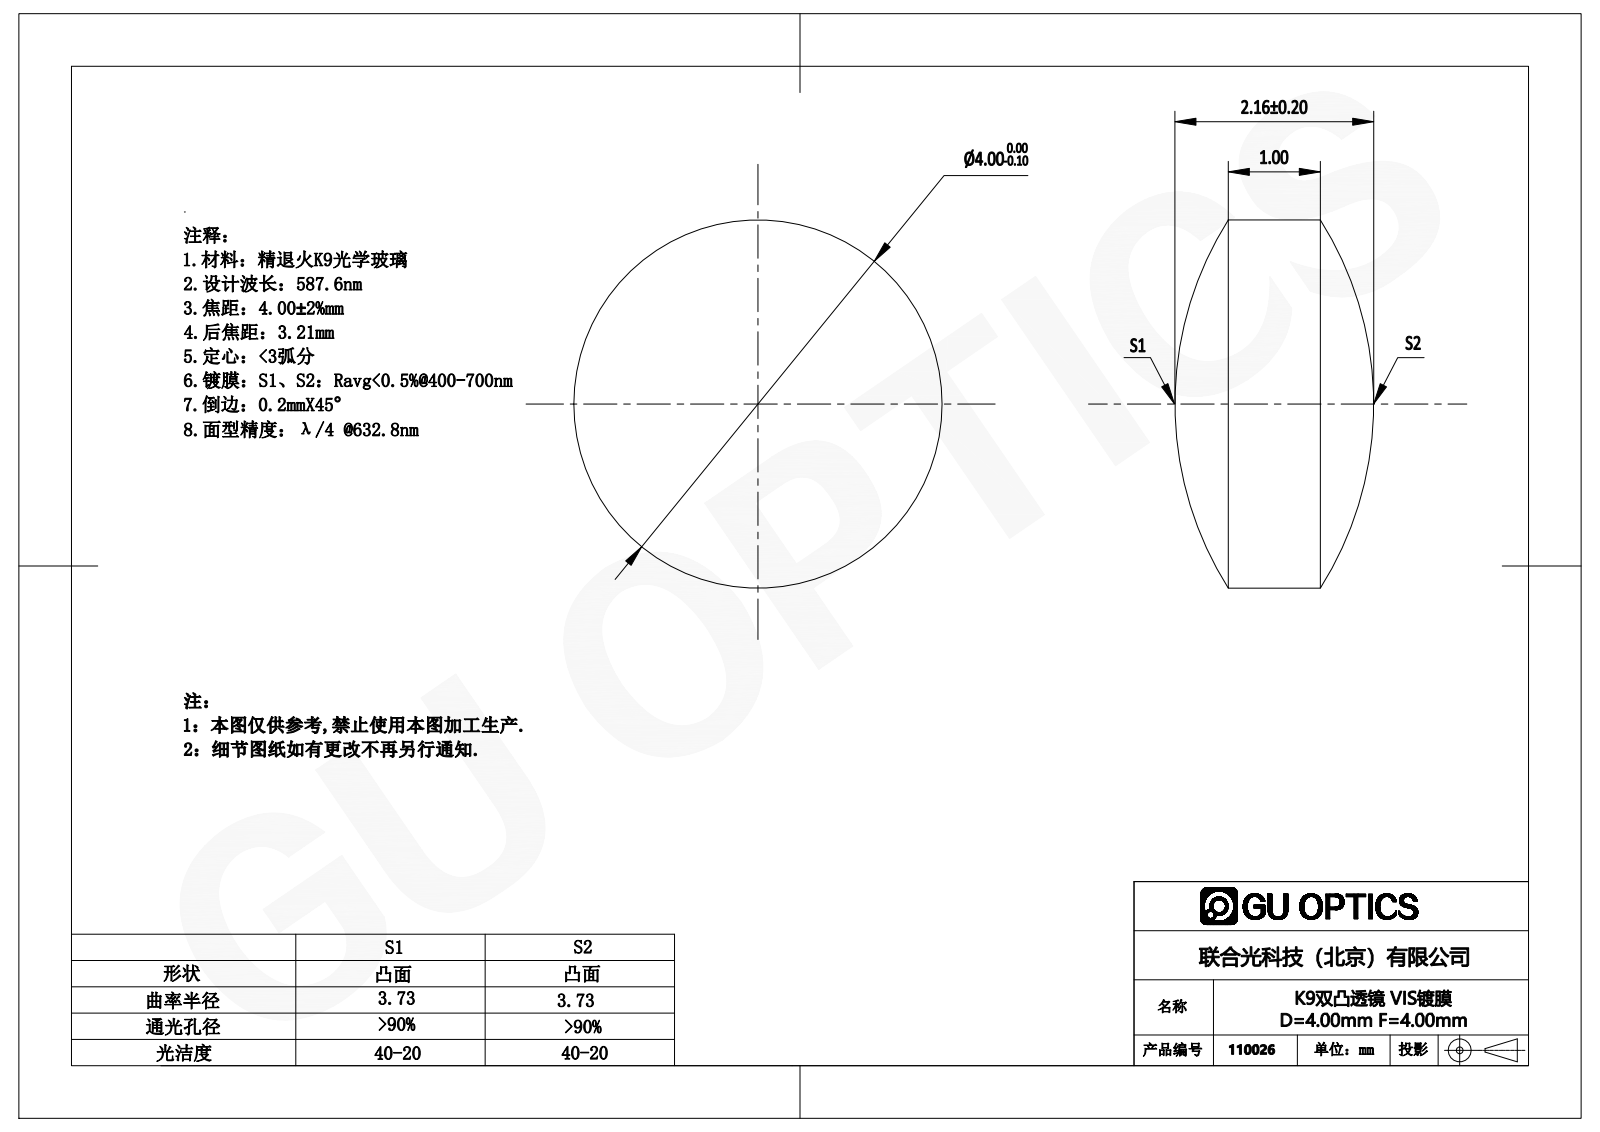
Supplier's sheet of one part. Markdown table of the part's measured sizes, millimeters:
| quantity | value |
| --- | --- |
| part name | 110004 |
| STEP written by | SolidWorks 2016 (CONFIG_CONTROL_DESIGN) |
| units | millimeters |
| bodies | 1 solid, 6 faces (0 planar, 2 cylindrical, 4 other) |
| overall size | 4 × 4 × 2.16 |
| volume | 20 mm³ |
| surface area | 40 mm² |
| round bosses / shafts (diameter × count) | 4 × 1 |
